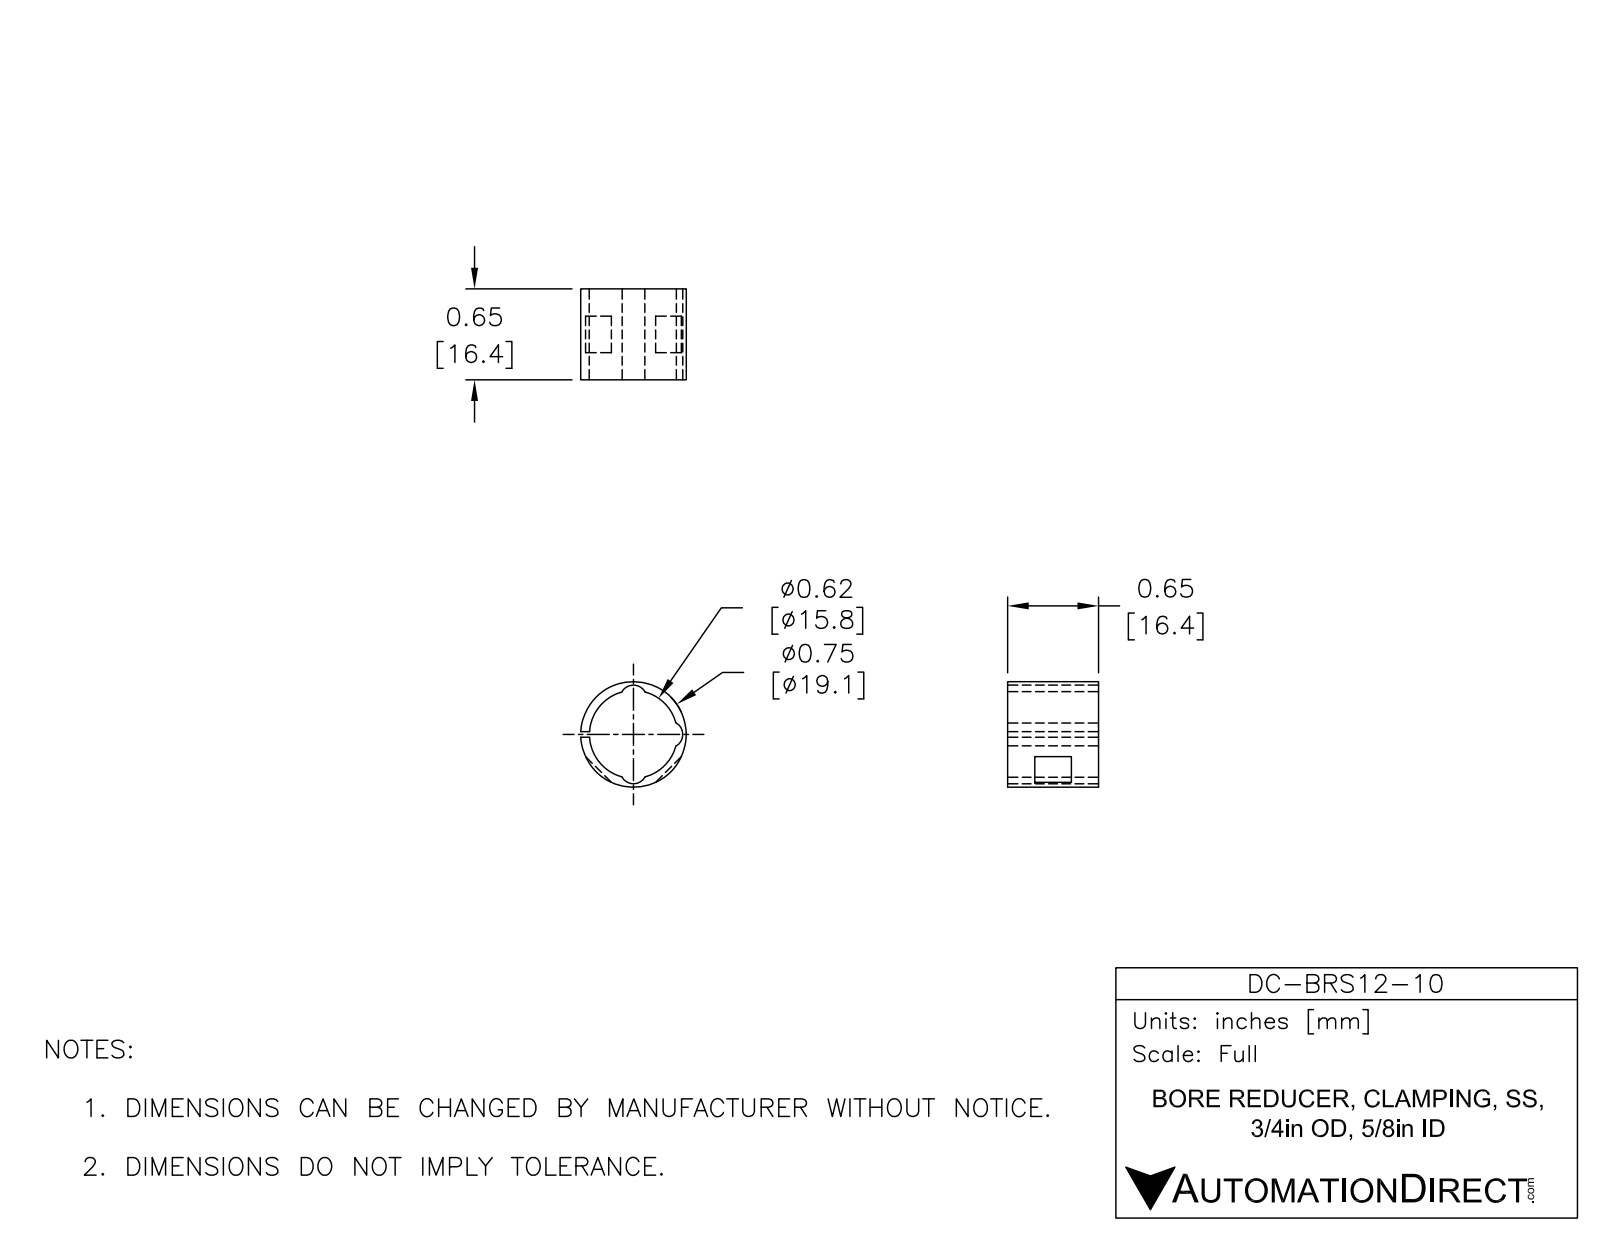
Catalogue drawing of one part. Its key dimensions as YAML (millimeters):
part_name: "DC-BRS12-10"
step_written_by: "SolidWorks 2015 (AUTOMOTIVE_DESIGN)"
units: millimeters
bodies: {solids: 1, faces: 21, planar: 10, cylindrical: 11, other: 0}
overall_size: [19.05, 19.04, 16.41]
volume: 1225
surface_area: 2024
round_bosses_or_shafts:
  - {diameter: 19.05, count: 1}
partial_cylinders:
  - {radius: 2.38, count: 3}
  - {radius: 7.94, count: 1}
face_to_face_distances: [16.4, 1.02, 4.9, 11.5, 6.6]
